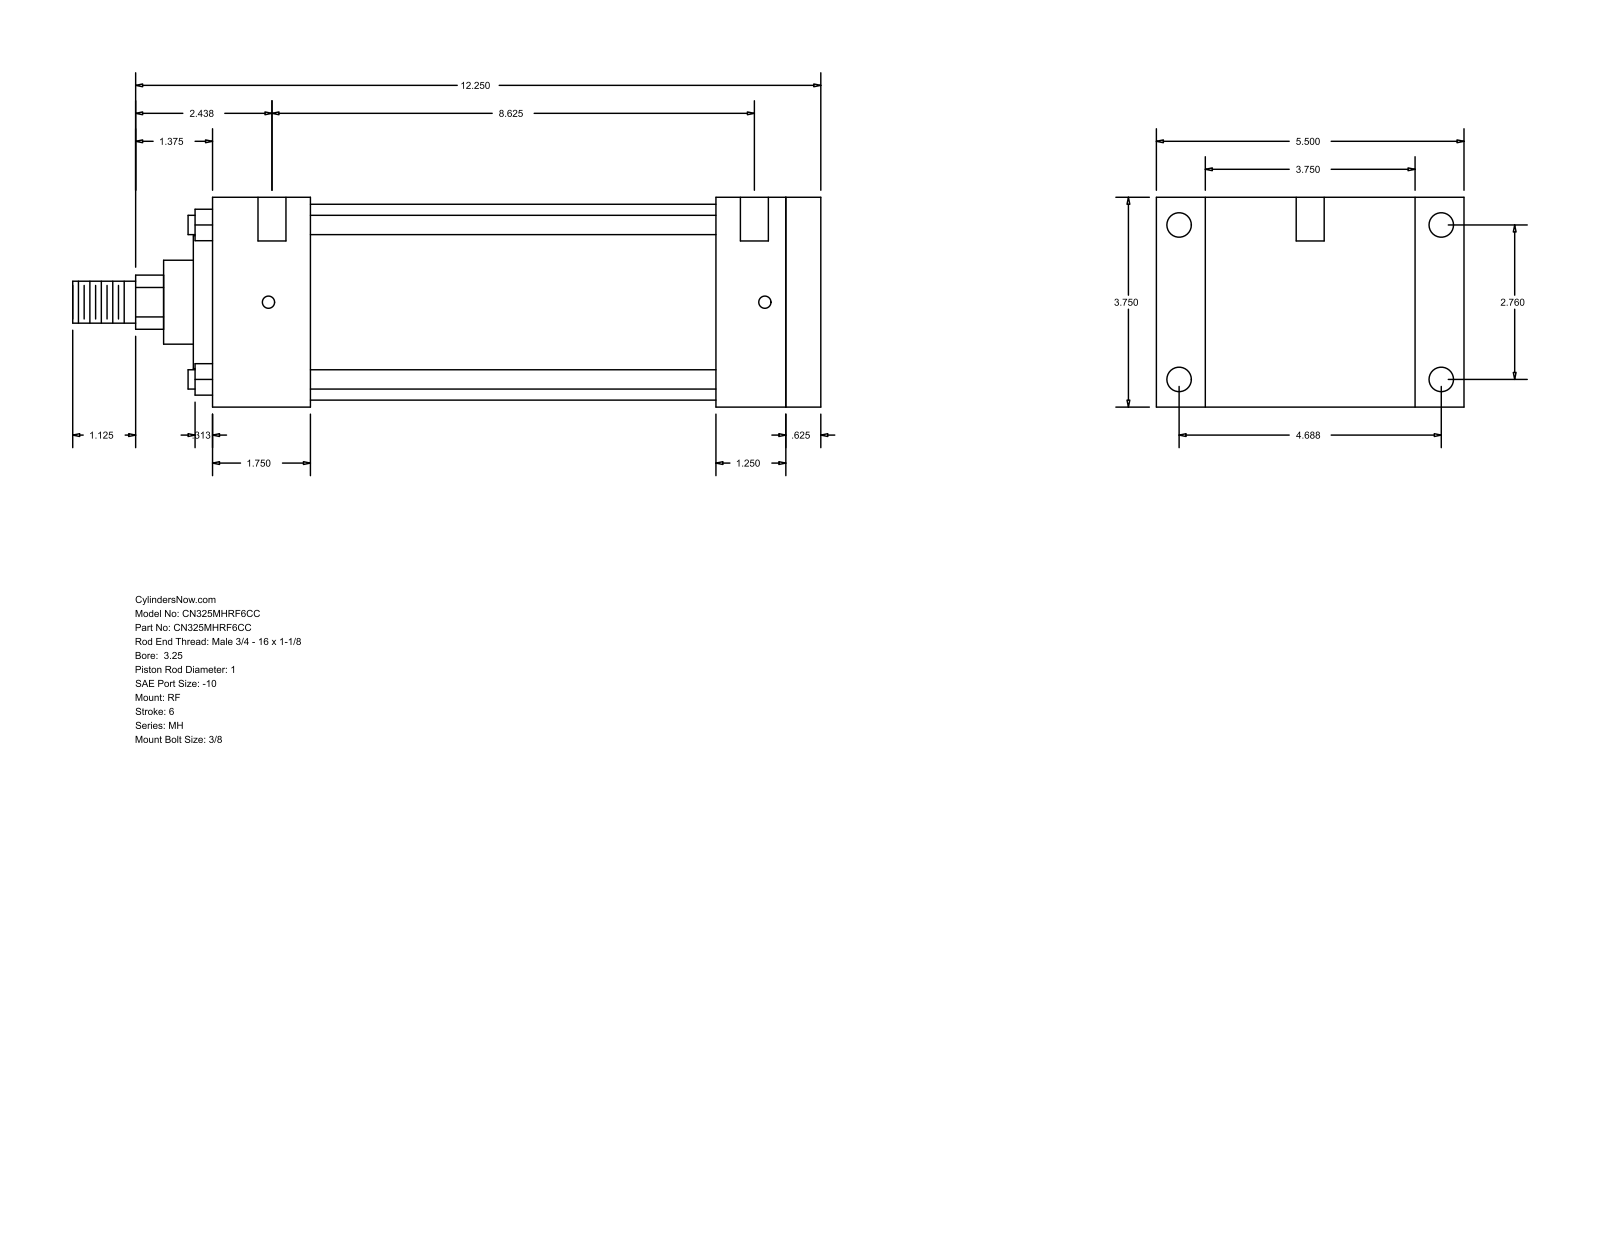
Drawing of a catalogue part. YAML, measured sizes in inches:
part_name: "MH_RF__0325_1"
step_written_by: "GSSL Pune (CONFIG_CONTROL_DESIGN)"
units: inches
bodies: {solids: 0, faces: 94, planar: 65, cylindrical: 29, other: 0}
overall_size: [13.375, 5.5, 3.75]
round_holes:
  - {diameter: 0.219, count: 4}
  - {diameter: 0.438, count: 4}
  - {diameter: 0.5, count: 2}
round_bosses_or_shafts:
  - {diameter: 0.345, count: 4}
  - {diameter: 3.5, count: 1}
  - {diameter: 2.375, count: 1}
  - {diameter: 1.5, count: 1}
  - {diameter: 1, count: 1}
  - {diameter: 0.75, count: 1}
partial_cylinders:
  - {radius: 0.484, count: 1}
face_to_face_distances: [3.75, 10.875, 10.25, 0.625, 0.875, 4.625, 1.75, 8.5, 9.125, 9]
hole_center_spacings: [2.76, 4.687, 5.439, 8.875, 0.062, 0.187, 8.625, 8.687]
